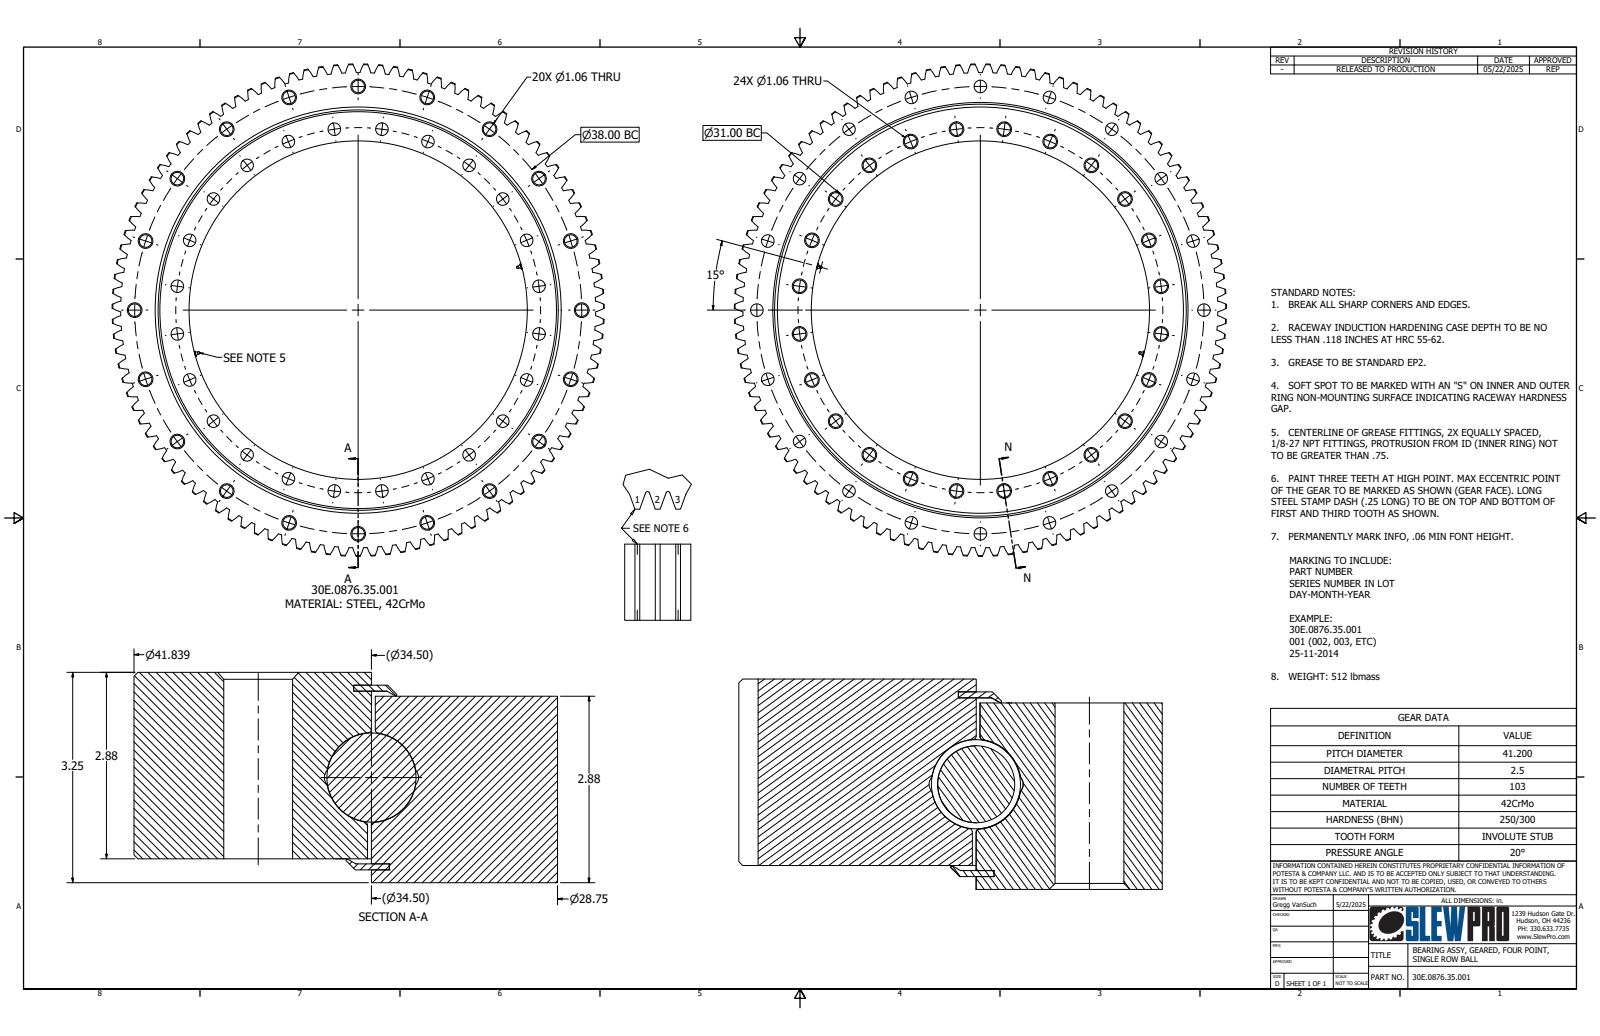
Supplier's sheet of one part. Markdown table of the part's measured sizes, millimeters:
| quantity | value |
| --- | --- |
| part name | 30E.0876.35.001; Spur Gears1; 1_8 NPT Fitting |
| STEP written by | Autodesk Inventor 2026 (AUTOMOTIVE_DESIGN) |
| units | millimeters |
| bodies | 8 solids, 905 faces (36 planar, 476 cylindrical, 393 other) |
| overall size | 1062.7 × 1062.6 × 82.6 |
| volume | 29 600 000 mm³ |
| surface area | 2 762 000 mm² |
| round holes (diameter × count) | 27 × 44, 2.5 × 2, 38.2 × 1, 730.3 × 1, 862.3 × 1, 879.3 × 1, 890.3 × 1 |
| round bosses / shafts (diameter × count) | 890.3 × 1, 876.3 × 1, 873.3 × 1, 862.3 × 1, 38.2 × 1 |
| partial cylindrical surfaces (radius × count) | 107.8 × 206, 512.6 × 1, 531.3 × 1 |
| main face-to-face distances | 73.2, 9.4, 82.6, 63.8, 68.1, 2, 70.1, 65.8, 4.3, 2.4 |
| hole center spacings | 393.7, 203.8, 556.8, 727.5, 760.6, 780.7, 681.9, 102.8 |
